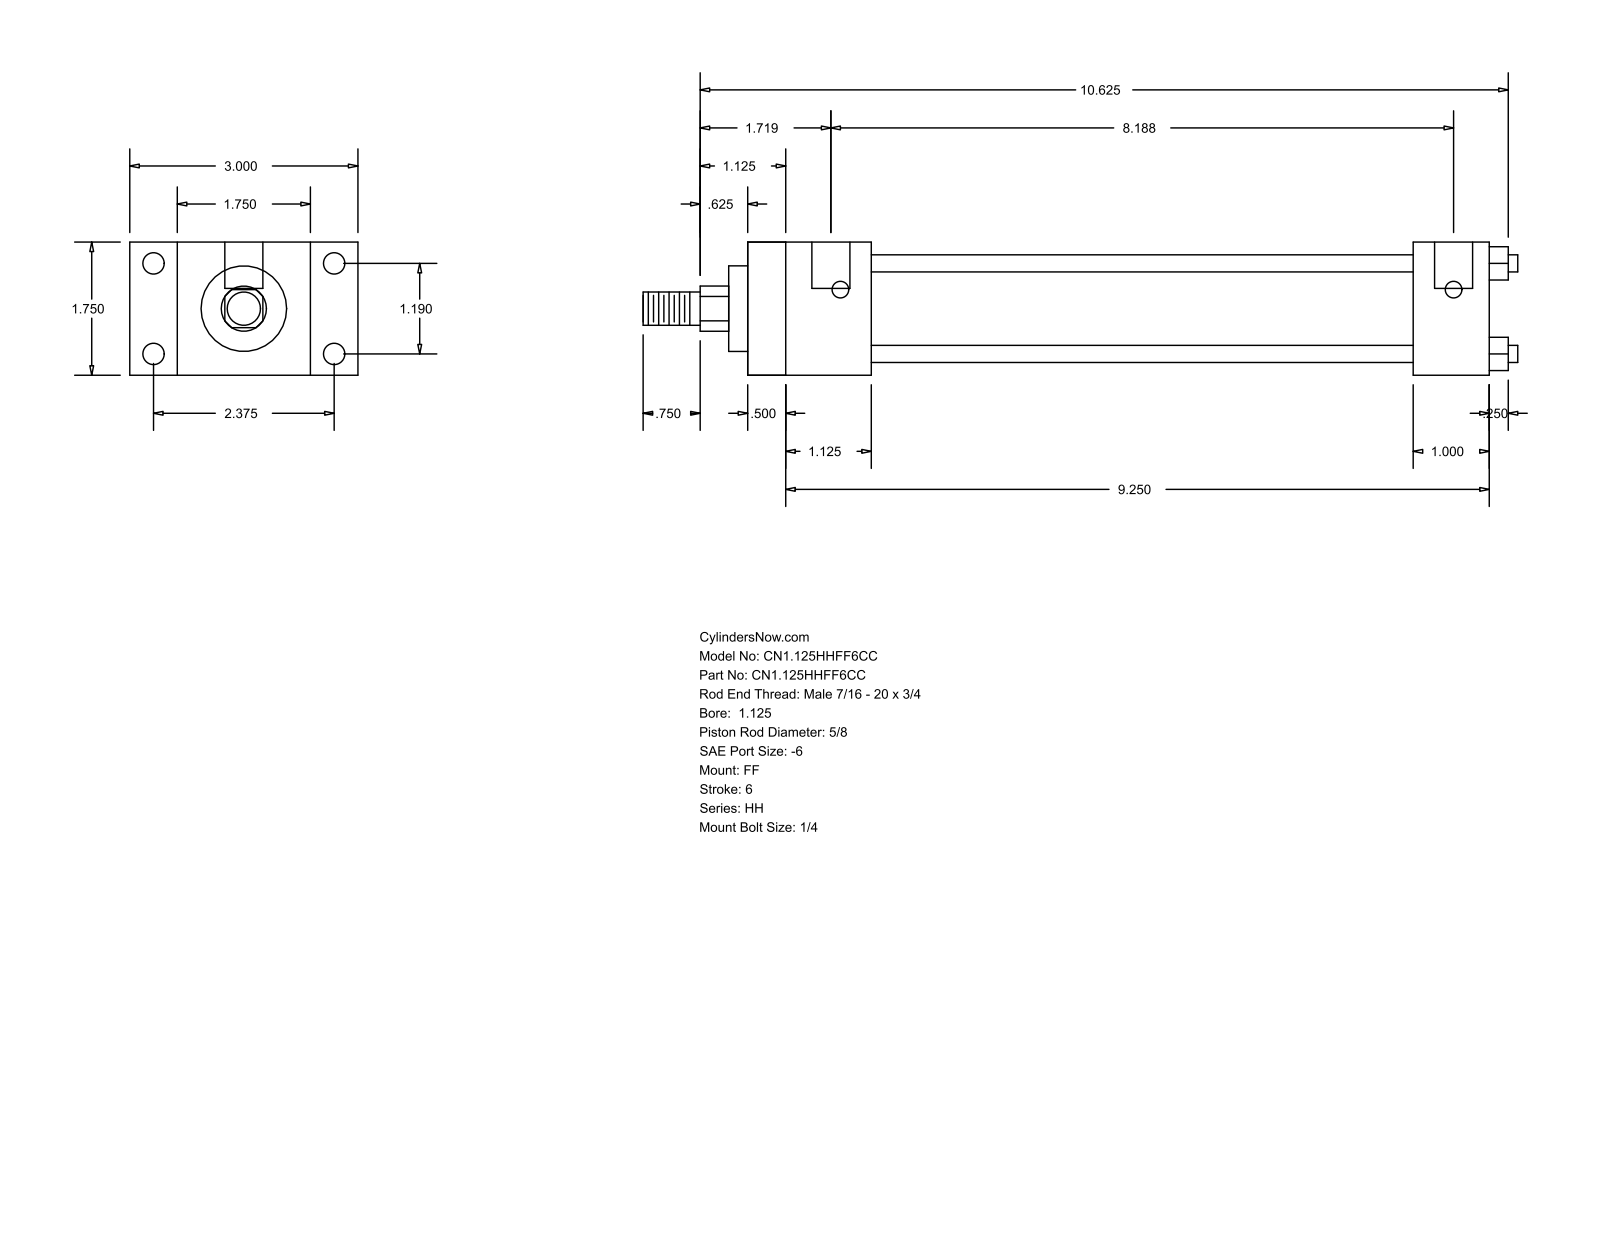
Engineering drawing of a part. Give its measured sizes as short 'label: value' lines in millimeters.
name: HH_FF__0112_0.625
written by: GSSL Pune (CONFIG_CONTROL_DESIGN)
unit: mm
bodies: 0 solids, 92 faces (64 planar, 28 cylindrical, 0 other)
size: 292.1 × 76.2 × 44.45
holes: 4× ⌀5.56, 4× ⌀7.14, 2× ⌀12.7
bosses: 4× ⌀5.71, 1× ⌀34.92, 1× ⌀28.57, 1× ⌀15.88, 1× ⌀11.11
rounds: 1× R7.54
face distances: 44.46, 247.64, 12.69, 234.95, 15.87, 28.58, 60.33, 25.4, 41.27, 222.24
hole spacings: 30.22, 60.32, 67.47, 204.79, 3.17, 207.96
